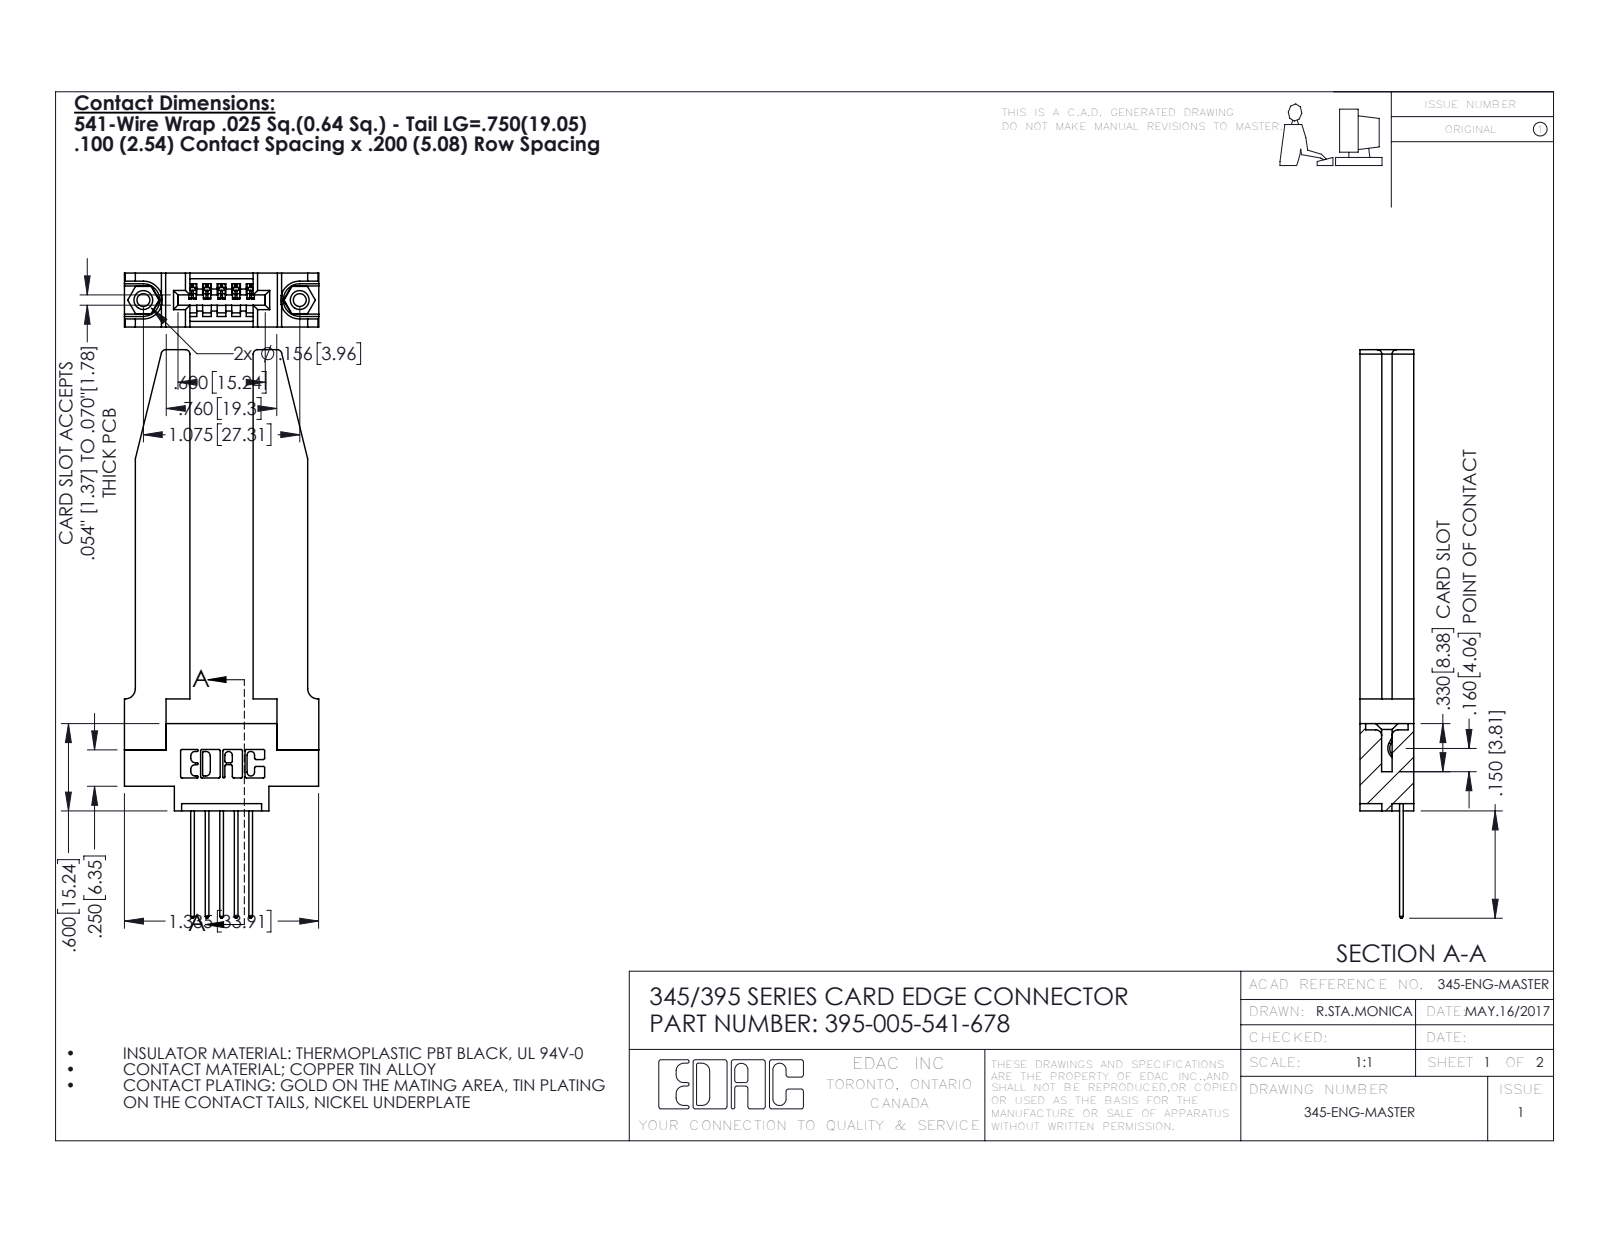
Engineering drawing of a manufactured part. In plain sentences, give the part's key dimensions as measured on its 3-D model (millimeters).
The part is named "345-292-001_345-293-141; 345-250-001_345-250-001-102; 345 Part_0.170 Offset - 0.156 Dia-TH; 345-220-078_345-220-078 (+1 more)". Its 3-D file was written by "SolidWorks 2016 (CONFIG_CONTROL_DESIGN)". It is 10 solids with 654 faces: 426 planar, 176 cylindrical and 52 other. Overall it measures 99.2 by 33.9 by 9.4 millimeters. Its volume is 10 600 cubic millimeters and its surface area 10 320 square millimeters. Round holes: 2 of diameter 2.3, 2 of diameter 3.2, 2 of diameter 4, 1 of diameter 1.6. Round bosses or shafts: 2 of diameter 3.9. Partial cylindrical surfaces (rounded edges, fillets, slot ends): 22 of radius 0.3, 10 of radius 0.2, 10 of radius 0.3, 8 of radius 0.8, 6 of radius 0.2, 6 of radius 0.8, 3 of radius 0.7, 2 of radius 0.8. The main face-to-face distances are 9.4, 3.8, 5.6, 11, 3.8, 1.8, 7.6, 2, 2.4, 1.8. The hole center spacings are 6.9, 21.5, 27.3.
